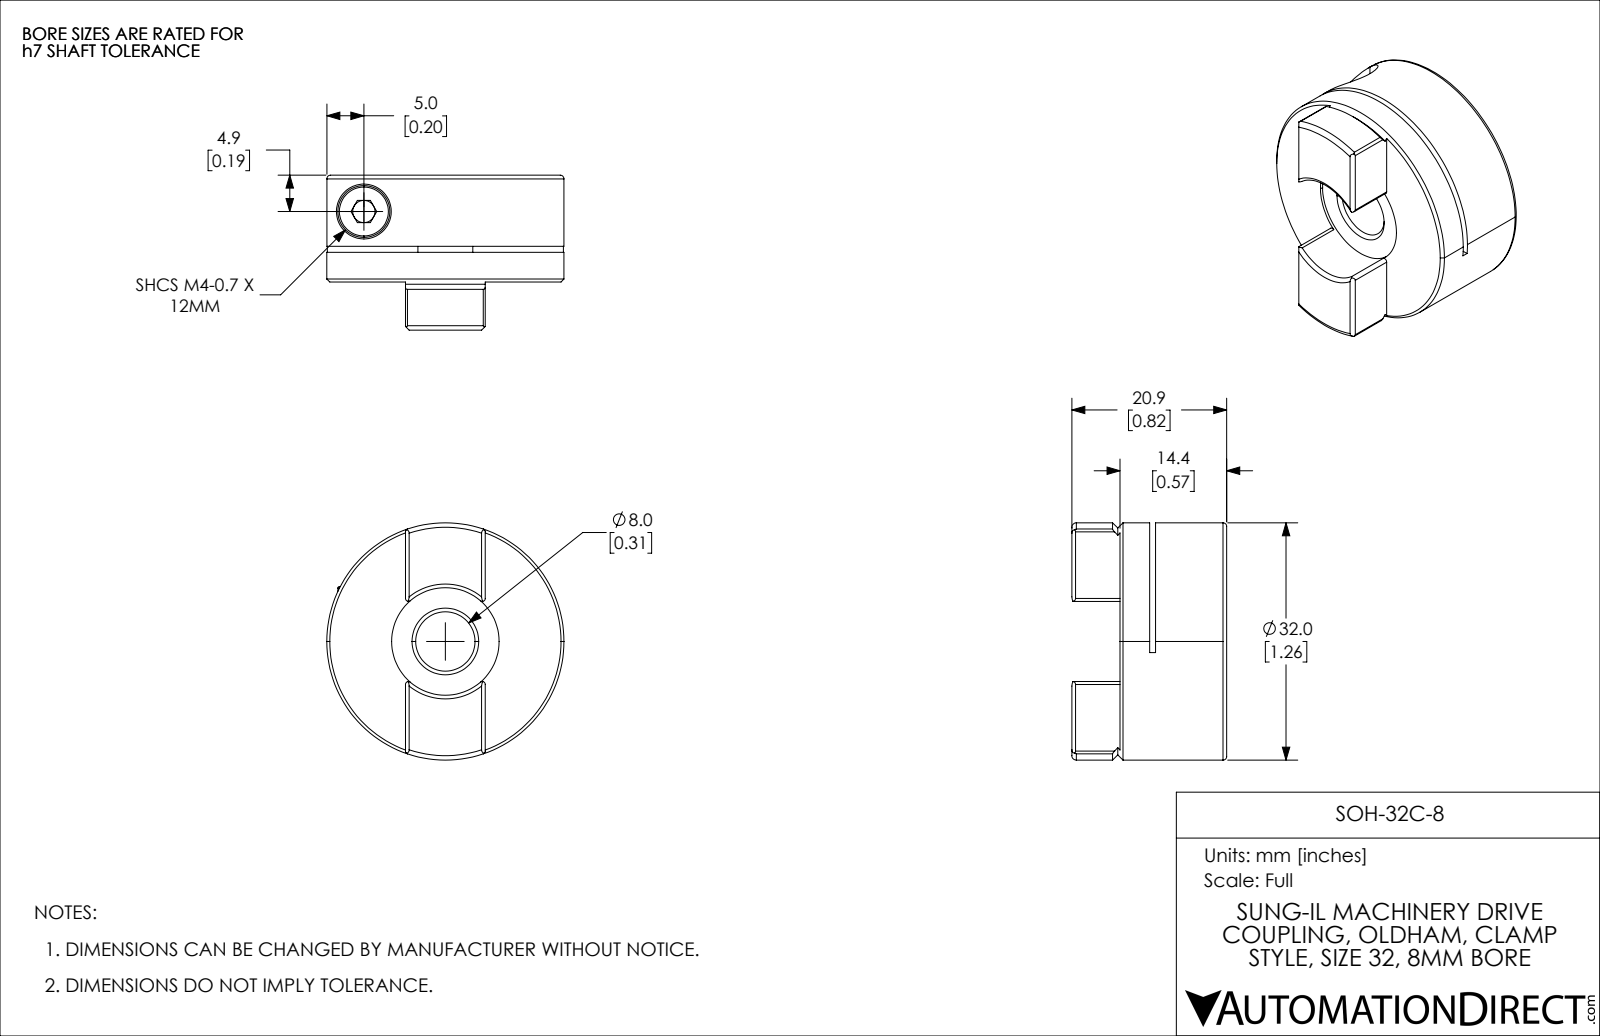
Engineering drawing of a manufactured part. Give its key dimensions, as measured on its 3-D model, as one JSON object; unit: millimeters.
{"part_name": "SOH-32C-8", "step_written_by": "SolidWorks 2021 (CONFIG_CONTROL_DESIGN)", "units": "millimeters", "bodies": {"solids": 2, "faces": 97, "planar": 39, "cylindrical": 33, "other": 25}, "overall_size": [32, 32, 20.9], "volume_mm3": 11350, "surface_area_mm2": 5480, "round_holes": [[3, 1], [3.3, 1], [4.4, 1], [7.4, 1], [8, 1], [14.5, 1]], "round_bosses_or_shafts": [[32, 1], [7, 1], [4, 1]], "partial_cylinders_radius": [[0.4, 8], [25, 1]], "face_to_face_distances": [4, 10.4, 14.4, 9.6, 0.8, 4.8, 1, 20.9, 11.3, 10.5]}
